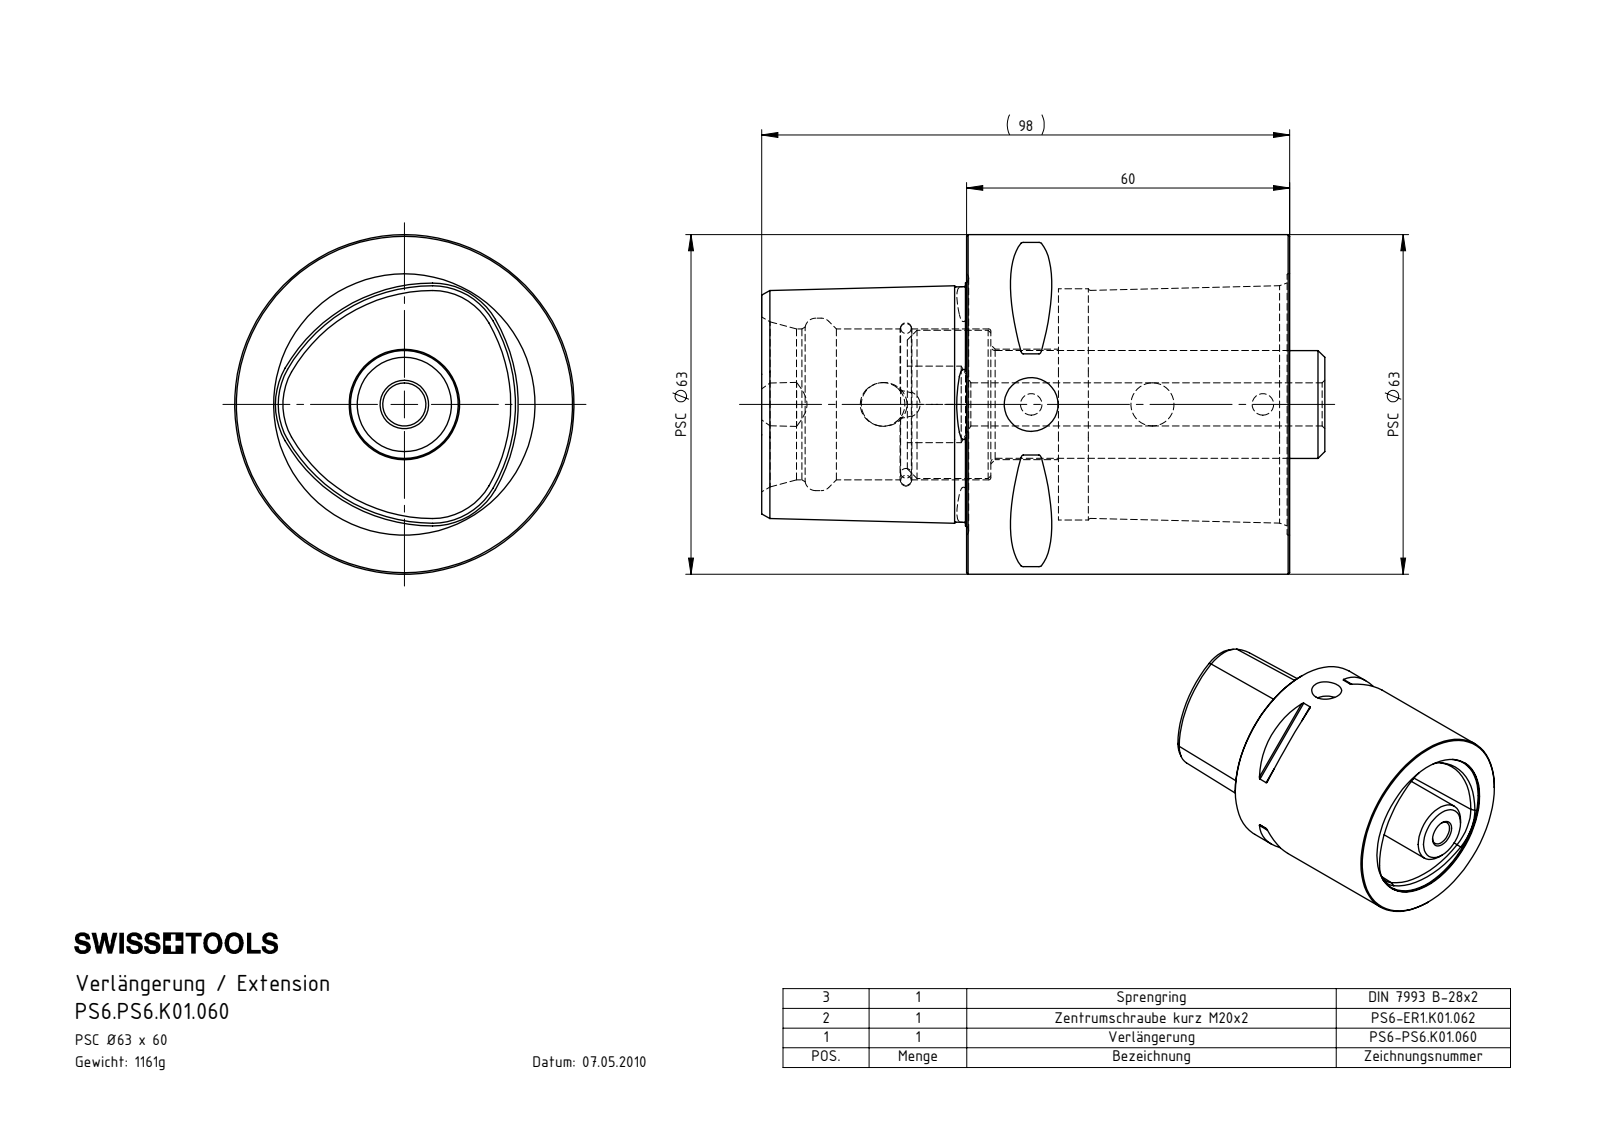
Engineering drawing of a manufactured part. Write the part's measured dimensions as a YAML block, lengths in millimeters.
part_name: "PS6.PS6.K01.060; ISO 8745-4x12_PreviewCfg; PS6-ER1.K01.062_A_PreviewCfg; PS6-PS6.K01.060_B"
step_written_by: "SolidWorks 2017 (AUTOMOTIVE_DESIGN)"
units: millimeters
bodies: {solids: 3, faces: 200, planar: 43, cylindrical: 46, other: 111}
overall_size: [104.5, 63, 63]
volume: 168162
surface_area: 41684
round_holes:
  - {diameter: 4, count: 2}
  - {diameter: 8, count: 2}
  - {diameter: 8.1, count: 1}
  - {diameter: 20.5, count: 1}
  - {diameter: 28, count: 1}
  - {diameter: 32, count: 1}
  - {diameter: 48.5, count: 1}
round_bosses_or_shafts:
  - {diameter: 63, count: 1}
  - {diameter: 26.8, count: 1}
  - {diameter: 20, count: 1}
partial_cylinders:
  - {radius: 0.5, count: 8}
  - {radius: 12.4, count: 3}
  - {radius: 30.5, count: 3}
  - {radius: 6, count: 1}
face_to_face_distances: [60, 17.05, 42.95, 38, 55.05, 98, 42.5, 4.5, 12.55, 55.5]
hole_center_spacings: [8, 14.5, 22.5, 27.5, 42, 50]
